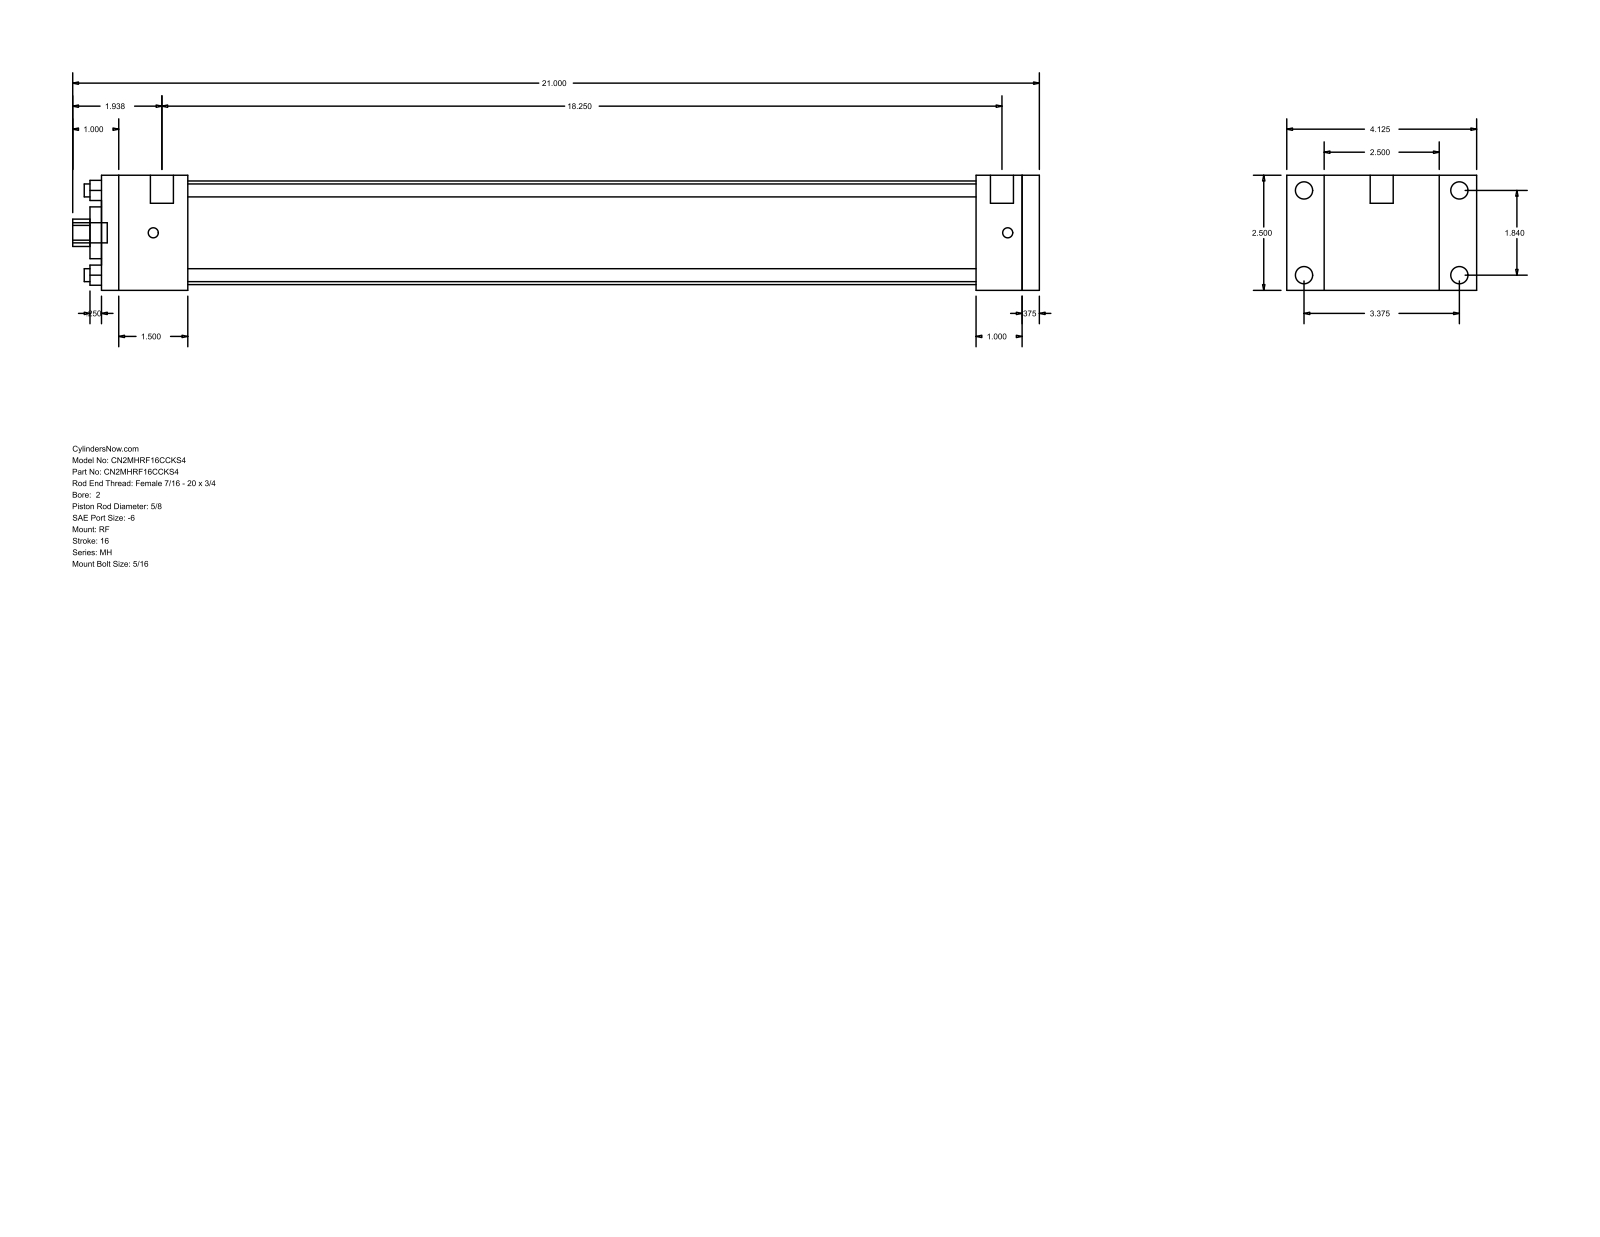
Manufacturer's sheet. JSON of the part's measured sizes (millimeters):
{"part_name": "MH_RF__0200_0.625", "step_written_by": "GSSL Pune (CONFIG_CONTROL_DESIGN)", "units": "millimeters", "bodies": {"solids": 0, "faces": 92, "planar": 64, "cylindrical": 28, "other": 0}, "overall_size": [533.4, 104.78, 63.5], "round_holes": [[7.14, 4], [15.88, 1], [28.57, 1], [57.15, 1]], "round_bosses_or_shafts": [[9.53, 4], [5.56, 4], [12.7, 2], [11.11, 1]], "partial_cylinders_radius": [[7.54, 1]], "face_to_face_distances": [63.5, 517.52, 9.52, 508, 25.4, 47.62, 482.6, 434.98, 460.38, 469.9], "hole_center_spacings": [33.05, 46.74, 66.1]}
